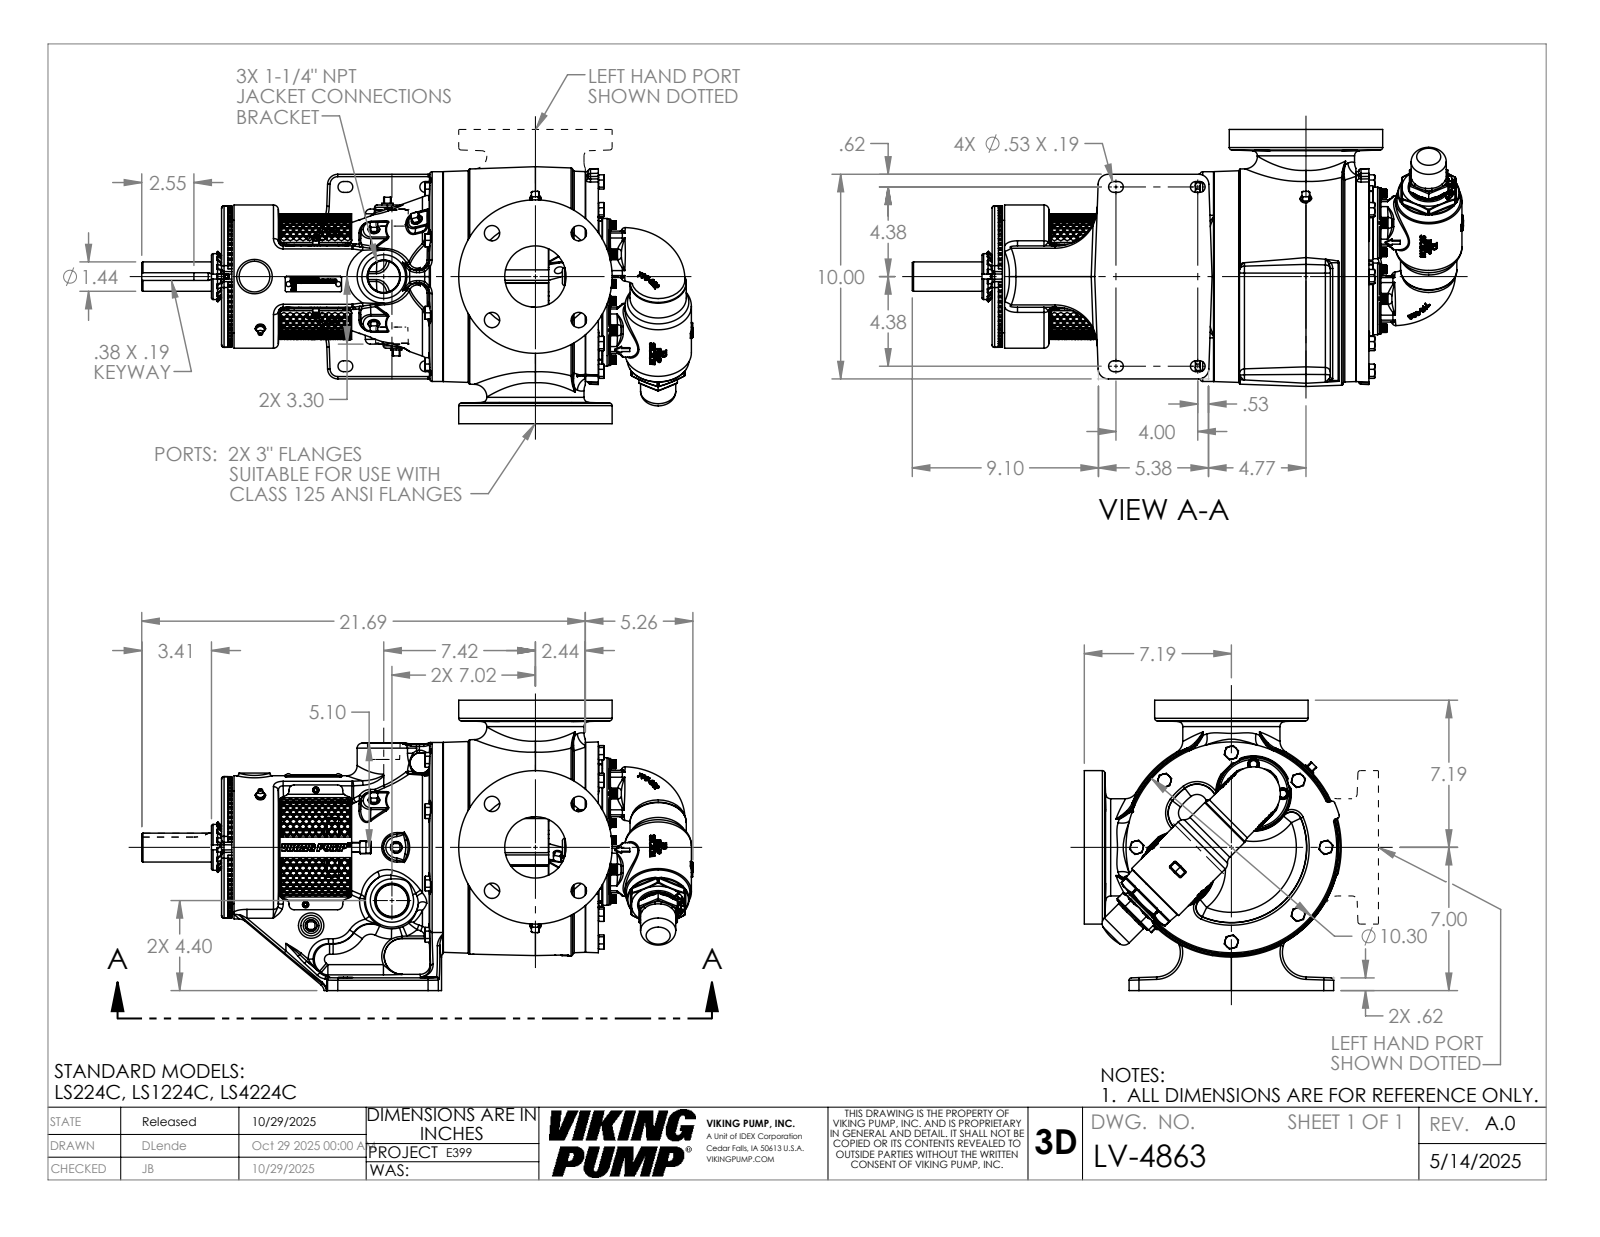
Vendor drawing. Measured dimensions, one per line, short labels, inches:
name: LV-4863
written by: SolidWorks 2024 (AUTOMOTIVE_DESIGN)
unit: in
bodies: 1 solid, 5218 faces (1738 planar, 987 cylindrical, 2493 other)
size: 26.944 × 14.19 × 12.56
volume: 1 216 in³; area: 1 521 in²
holes: 8× ⌀0.75, 8× ⌀1.094, 6× ⌀0.199, 6× ⌀0.25, 3× ⌀0.159, 2× ⌀0.266, 2× ⌀0.313, 1× ⌀1.506, 1× ⌀1.552, 1× ⌀1.577, 1× ⌀1.593, 1× ⌀1.83
bosses: 10× ⌀0.625, 8× ⌀0.563, 6× ⌀0.625, 3× ⌀3.5, 3× ⌀0.437, 3× ⌀0.312, 2× ⌀7.5, 2× ⌀4.75
rounds: 109× R0.063, 74× R0.069, 58× R0.12, 30× R0.03, 28× R0.5, 16× R0.24, 16× R0.45, 12× R0.25
face distances: 14.19, 1.5, 15.669, 3.539, 12.13, 0.5, 2.25, 2.141, 5.68, 17.81
hole spacings: 3, 4.243, 1.375, 2.18, 3.609, 4.446, 4.625, 6.404
